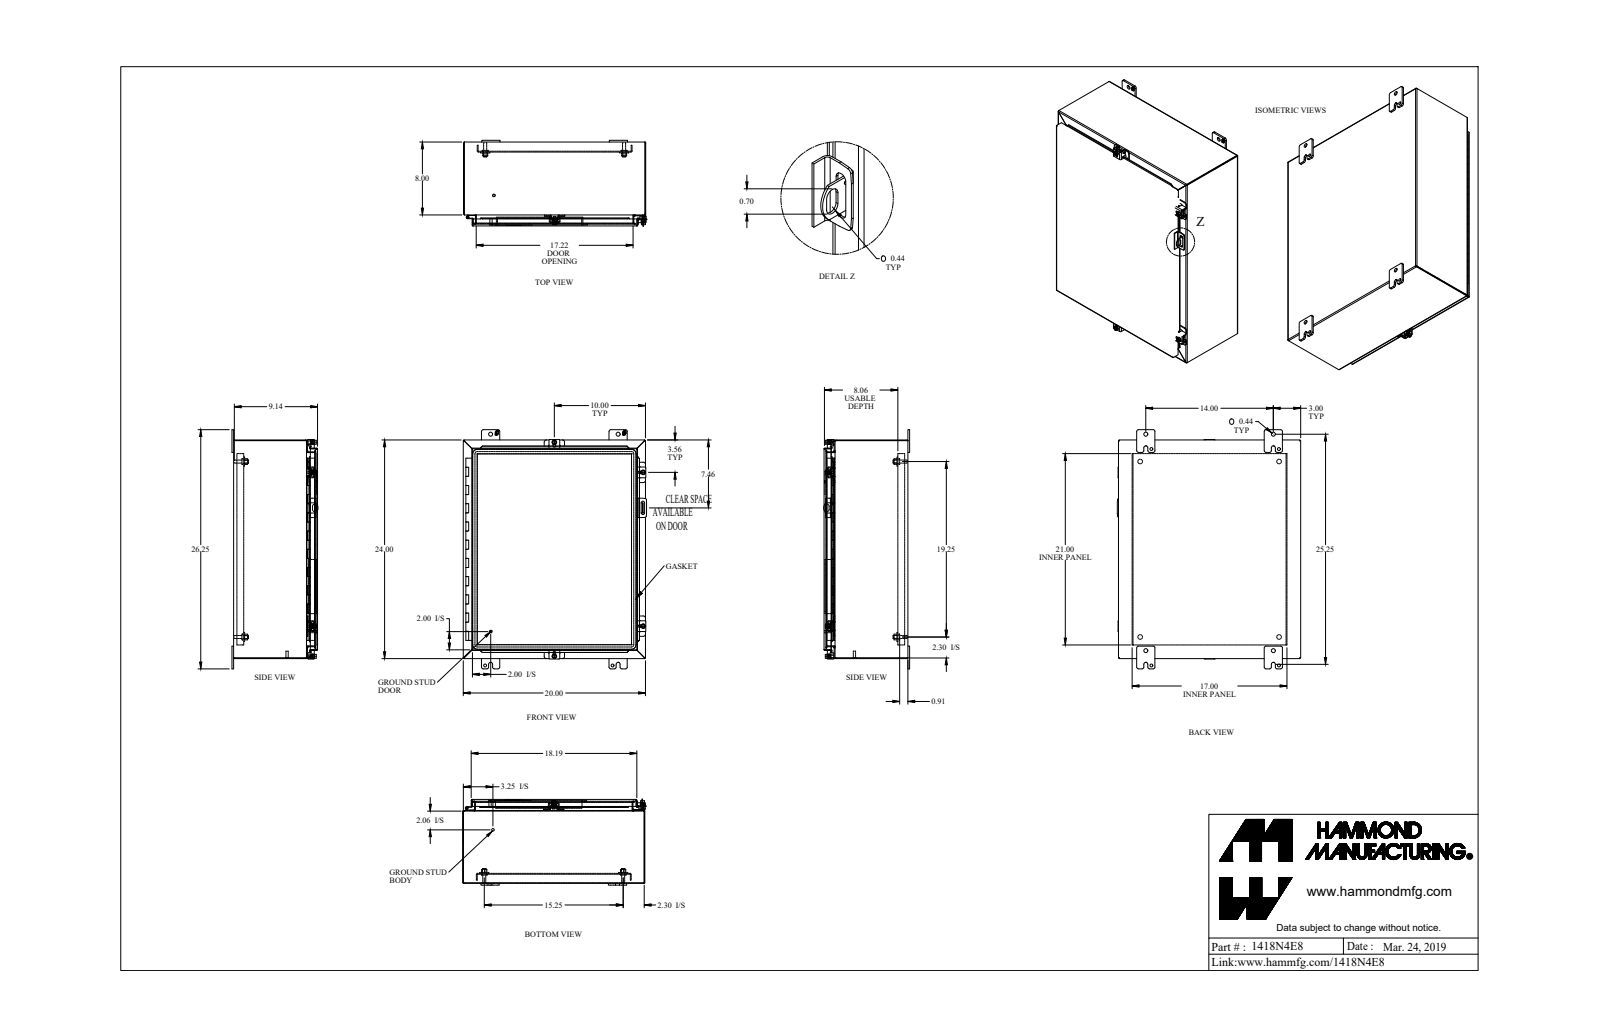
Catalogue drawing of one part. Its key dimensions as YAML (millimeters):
part_name: "1418N4E8_Default"
step_written_by: "SolidWorks 2019 (CONFIG_CONTROL_DESIGN)"
units: millimeters
bodies: {solids: 39, faces: 1413, planar: 853, cylindrical: 475, other: 85}
overall_size: [666.8, 511.2, 239.7]
volume: 3046000
surface_area: 3145000
round_holes:
  - {diameter: 5.4, count: 4}
  - {diameter: 8, count: 4}
  - {diameter: 9.5, count: 4}
  - {diameter: 11.1, count: 4}
  - {diameter: 12.7, count: 4}
  - {diameter: 6.7, count: 2}
  - {diameter: 6.7, count: 2}
  - {diameter: 7.8, count: 2}
  - {diameter: 11.3, count: 2}
  - {diameter: 3.2, count: 1}
  - {diameter: 4.7, count: 1}
round_bosses_or_shafts:
  - {diameter: 16.5, count: 4}
  - {diameter: 12.7, count: 4}
  - {diameter: 9.9, count: 4}
  - {diameter: 9.5, count: 4}
  - {diameter: 8.4, count: 4}
  - {diameter: 6.2, count: 4}
  - {diameter: 25.4, count: 2}
  - {diameter: 7.1, count: 2}
partial_cylinders:
  - {radius: 4.8, count: 26}
  - {radius: 0.9, count: 24}
  - {radius: 2.7, count: 24}
  - {radius: 1.2, count: 21}
  - {radius: 3.6, count: 21}
  - {radius: 6.4, count: 20}
  - {radius: 3.2, count: 10}
  - {radius: 1.1, count: 8}
face_to_face_distances: [1.8, 1.8, 230.3, 232.1, 232.1, 233.9, 2.4, 506.2, 205.9, 204.1]
hole_center_spacings: [623.8, 201.1, 355.6, 489, 576.4, 61.8, 201, 373.4]
